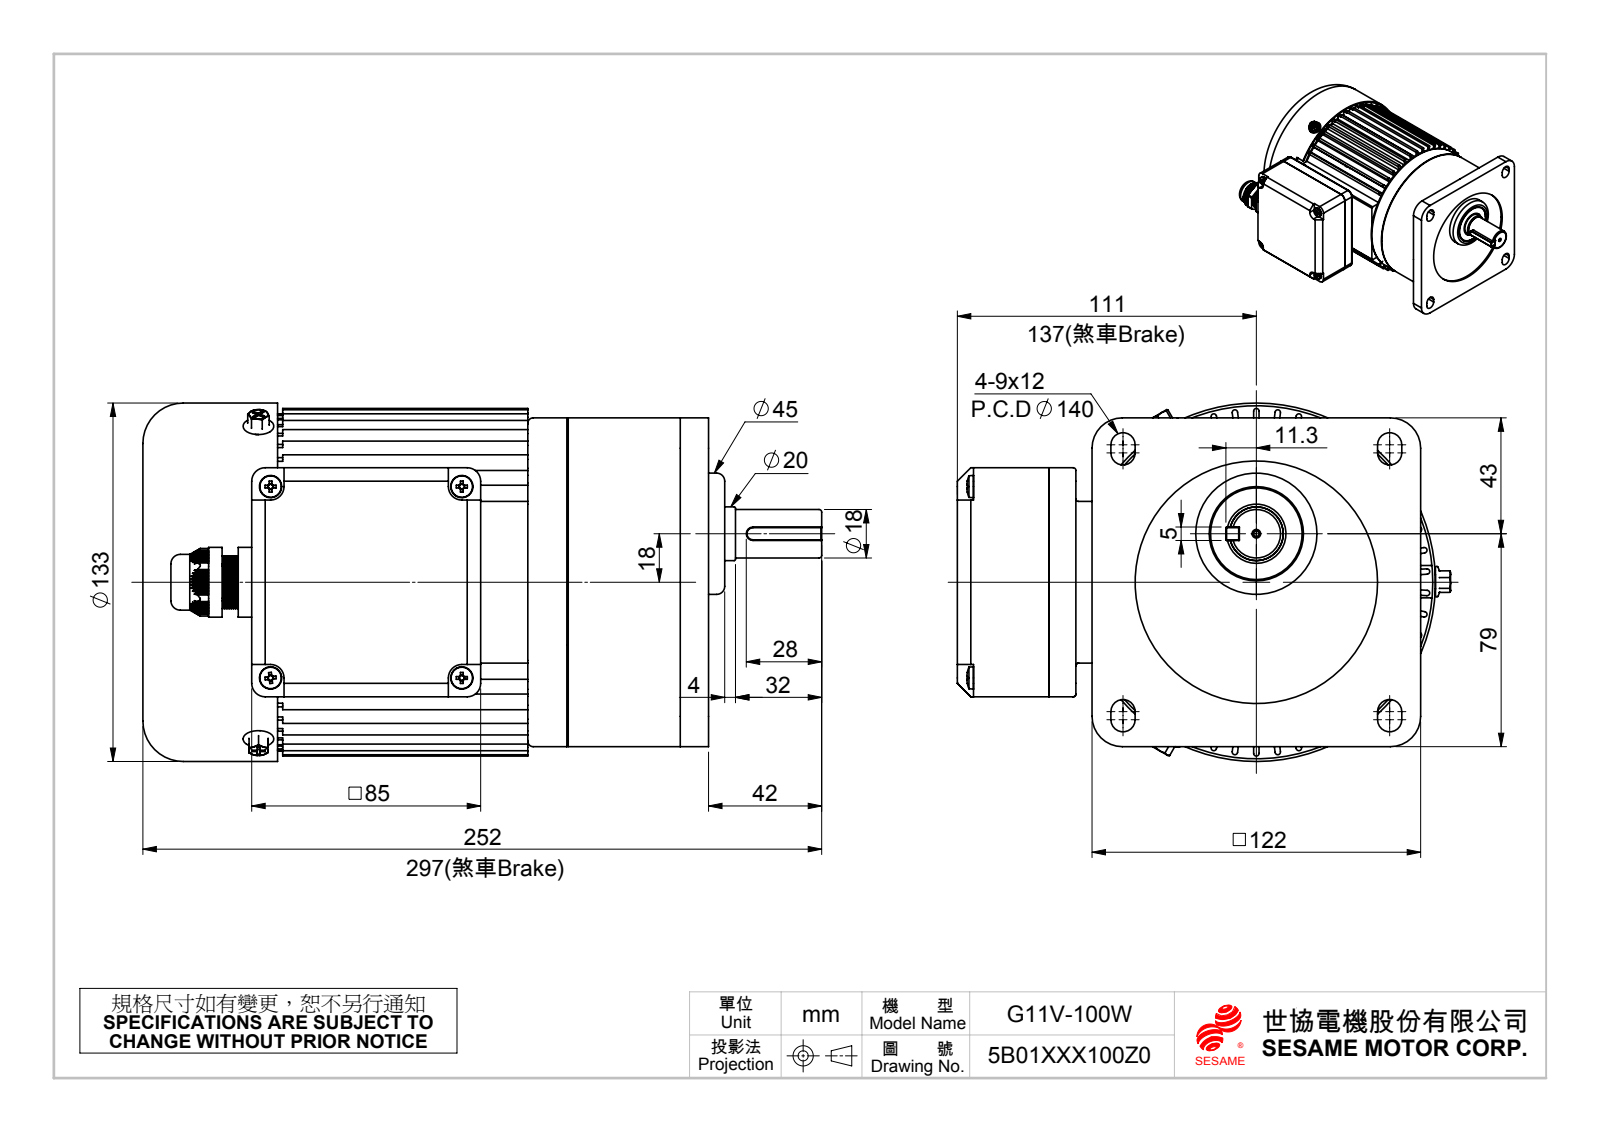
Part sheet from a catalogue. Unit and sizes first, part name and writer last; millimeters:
Units: millimetres
Overall size (bounding box): 252 × 183.11 × 133
Round holes (diameter × count): ⌀5 ×11, ⌀3.3 ×9, ⌀8 ×4, ⌀4.2 ×3, ⌀2 ×1, ⌀7.5 ×1, ⌀10.8 ×1, ⌀16.5 ×1, ⌀20 ×1, ⌀22 ×1, ⌀33 ×1, ⌀35 ×1
Round bosses / shafts (diameter × count): ⌀8.3 ×4, ⌀4 ×4, ⌀5 ×3, ⌀133 ×1, ⌀131 ×1, ⌀122 ×1, ⌀110.4 ×1, ⌀110 ×1
Partial cylindrical surfaces — rounded edges, fillets, slot ends (radius × count): R1 ×74, R1.03 ×8, R4.5 ×8, R5 ×8, R2.75 ×6, R2 ×4, R2.55 ×4, R3.55 ×4
Main face-to-face distances: 2, 3, 92, 10, 20, 115, 95, 159.1, 125, 105
Hole centre spacings: 45, 71, 11, 11.5, 14.66, 14.79, 17.36, 19.47
Volume: 2 422 000 mm³ · Surface area: 354 040 mm²
Bodies: 19 solids, 2602 faces (788 planar, 814 cylindrical, 1000 other)
Part name (STEP PRODUCT): 5x5xL_28L; 100W風扇蓋131x50／缺口70(直角); G11OS1; 外六角內十字螺絲M5 x 10_ISO 4162 - M5 x 10 x 10-N (+8 more)
STEP written by: SolidWorks 2010 (CONFIG_CONTROL_DESIGN)
